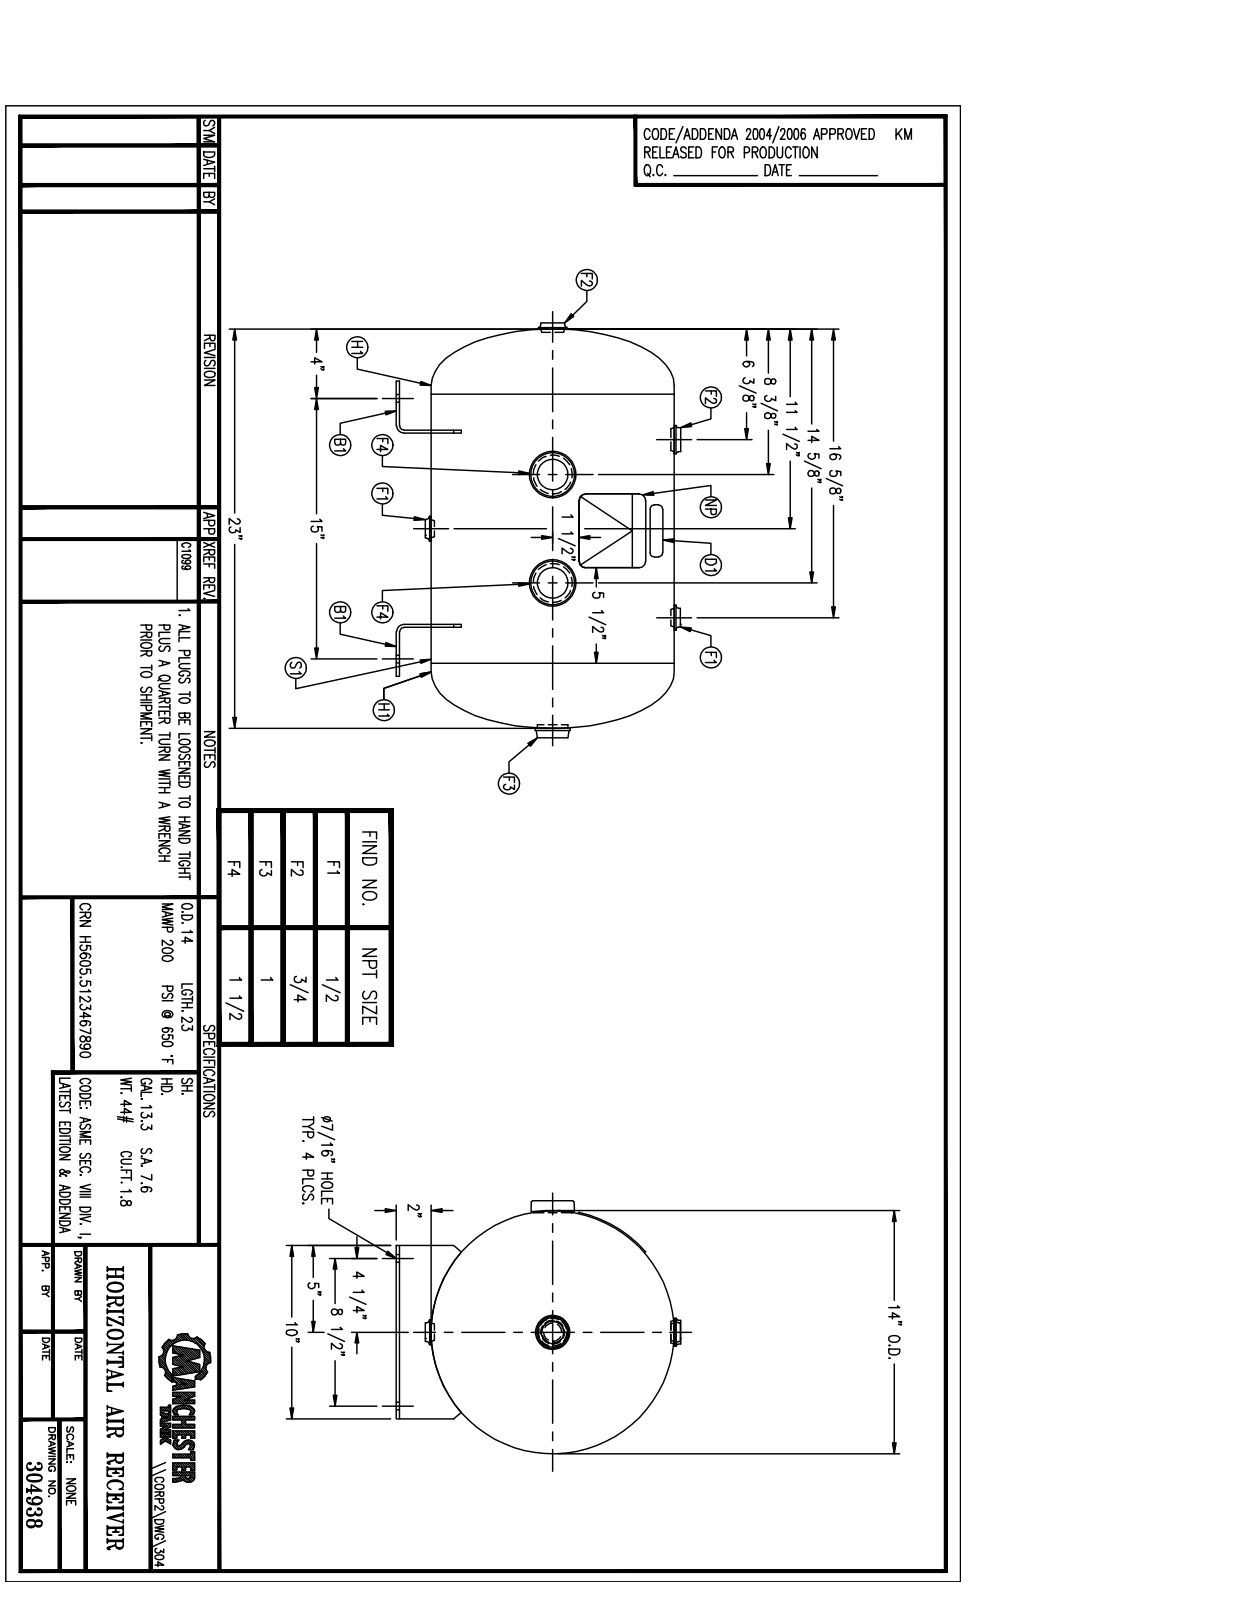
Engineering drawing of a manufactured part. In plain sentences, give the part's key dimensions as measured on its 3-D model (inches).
The part is named "304938". Its 3-D file was written by "SolidWorks 2011 (CONFIG_CONTROL_DESIGN)". It is 0 solids with 242 faces: 106 planar, 60 cylindrical and 76 other. Overall it measures 25.111 by 16.848 by 15.385 inches. Round holes: 4 of diameter 0.437. Round bosses or shafts: 2 of diameter 2.688, 2 of diameter 1.9, 2 of diameter 1.63, 2 of diameter 1.625, 2 of diameter 1.45, 2 of diameter 1.438, 2 of diameter 1.05, 2 of diameter 0.84. Partial cylindrical surfaces (rounded edges, fillets, slot ends): 2 of radius 0.25, 2 of radius 0.422, 1 of radius 7.06. The main face-to-face distances are 0.172, 0.172, 11.172, 11.344, 11, 2.25, 2.078, 13.25, 13.422, 0.75. The hole center spacings are 8.5, 15, 17.241.
